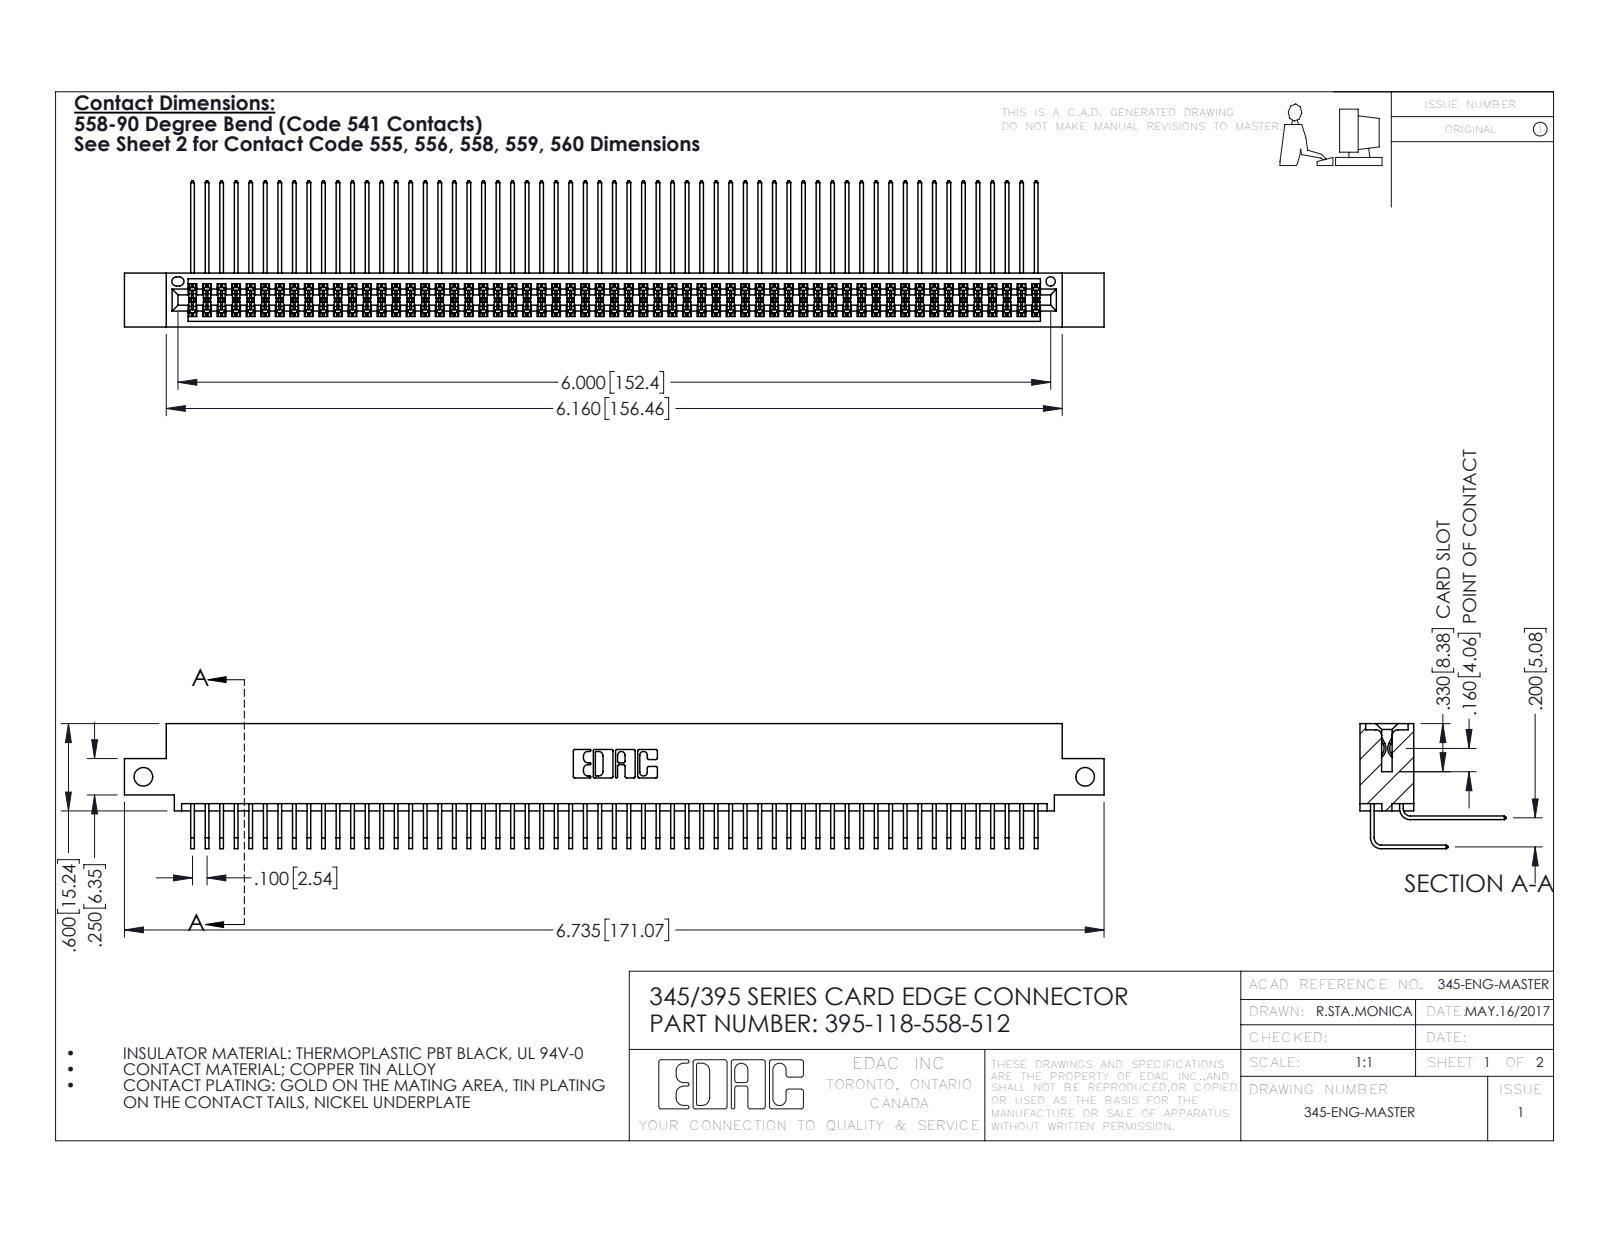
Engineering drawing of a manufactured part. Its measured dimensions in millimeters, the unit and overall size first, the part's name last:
Units: millimetres
Overall size (bounding box): 171.1 × 25.5 × 21.8
Round holes (diameter × count): ⌀3.3 ×2, ⌀1.6 ×1
Partial cylindrical surfaces — rounded edges, fillets, slot ends (radius × count): R0.2 ×178, R0.3 ×22, R0.2 ×6, R0.8 ×6, R0.7 ×3, R0.4 ×2, R0.5 ×2, R0.6 ×2
Main face-to-face distances: 1.8, 7.6, 5.1, 9.4, 2.5, 6.9, 0.6, 5.7, 0.6, 4.4
Hole centre spacings: 164.5
Volume: 17 290 mm³ · Surface area: 29 050 mm²
Bodies: 119 solids, 6266 faces (4214 planar, 2052 cylindrical, 0 other)
Part name (STEP PRODUCT): 395-118-558-512; 345 Part_0.110 Offset - Side Mount; 345-292-001_558 Tail - 2; 345-292-001_558 559 Tail - 1
STEP written by: SolidWorks 2016 (CONFIG_CONTROL_DESIGN)
